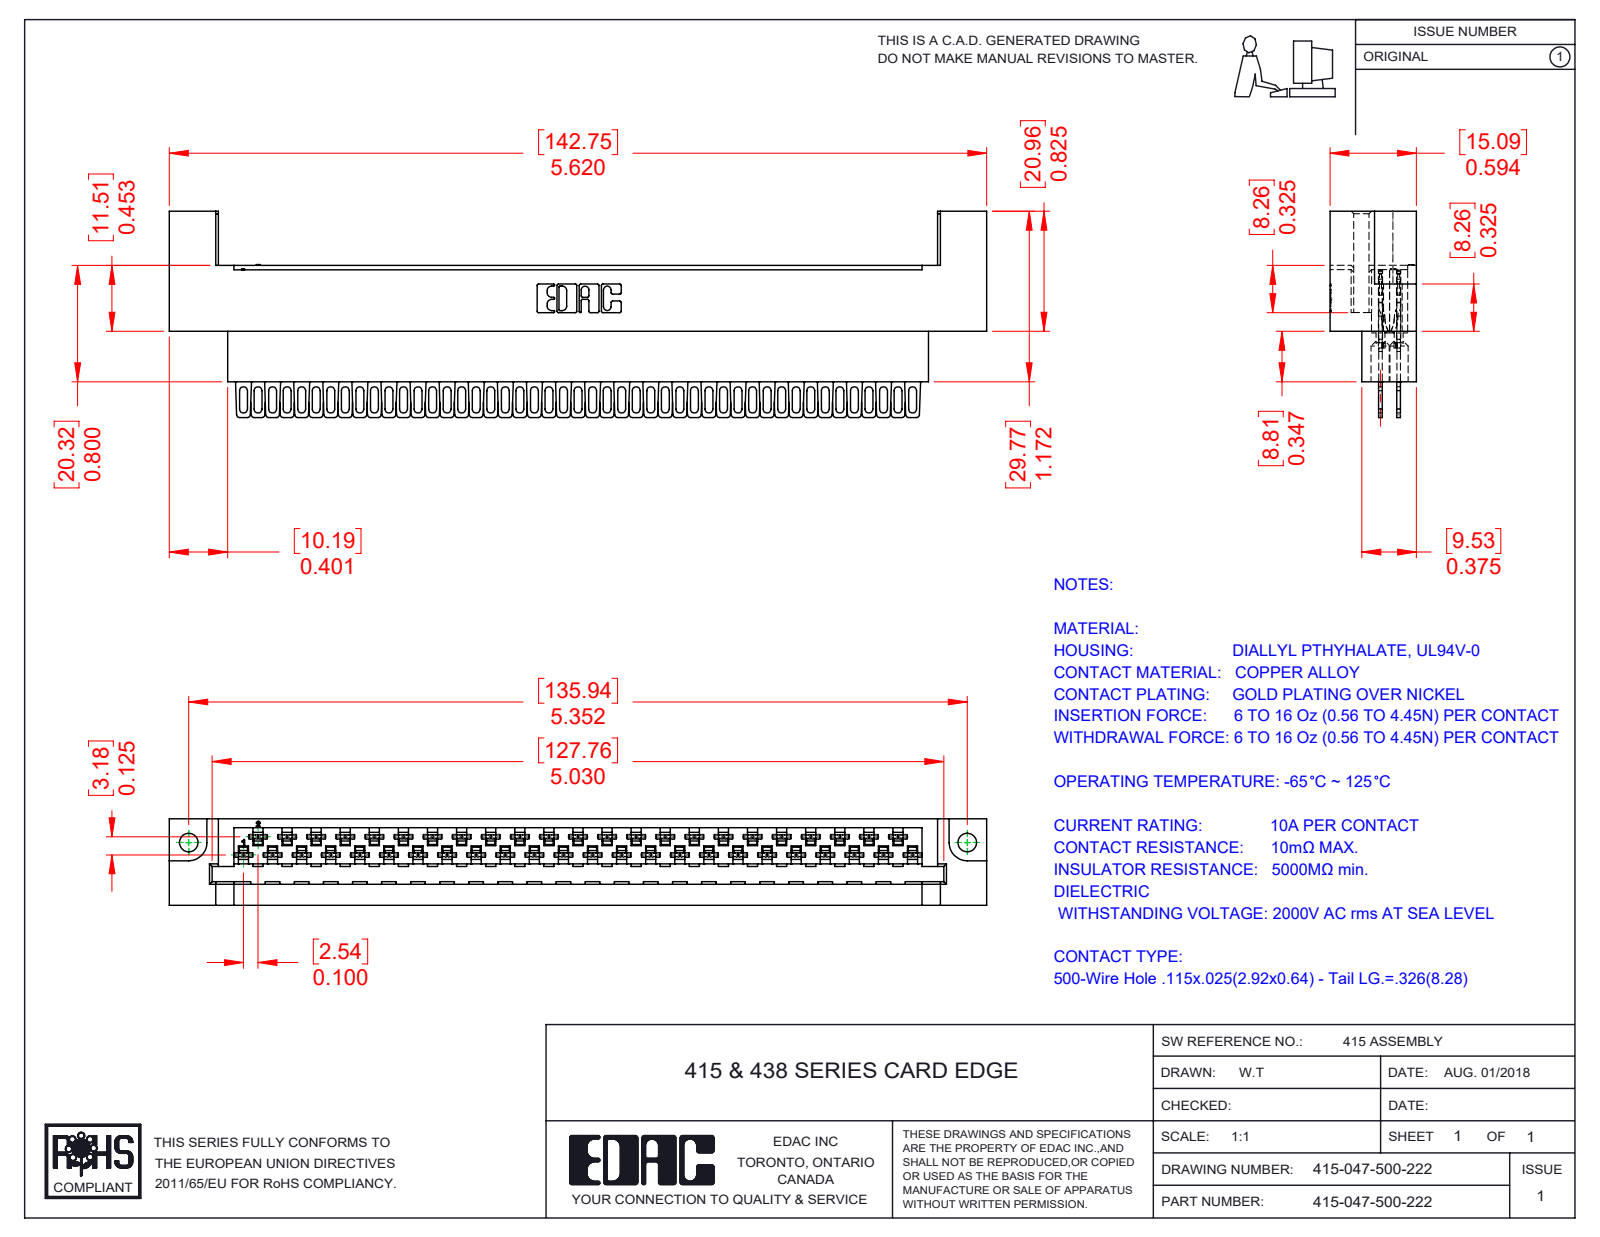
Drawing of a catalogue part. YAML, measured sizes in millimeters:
part_name: "415-047-500-222; 516-290-001_500; 415-210-001_415-210-047-222"
step_written_by: "SolidWorks 2016 (CONFIG_CONTROL_DESIGN)"
units: millimeters
bodies: {solids: 48, faces: 4956, planar: 3102, cylindrical: 1409, other: 445}
overall_size: [142.75, 36, 15.09]
volume: 27122
surface_area: 31647
round_holes:
  - {diameter: 1.27, count: 47}
  - {diameter: 3.3, count: 47}
  - {diameter: 3.25, count: 2}
partial_cylinders:
  - {radius: 0.3, count: 188}
  - {radius: 0.56, count: 188}
  - {radius: 0.18, count: 94}
  - {radius: 0.2, count: 94}
  - {radius: 0.41, count: 94}
  - {radius: 0.51, count: 94}
  - {radius: 0.69, count: 94}
  - {radius: 2.03, count: 94}
face_to_face_distances: [3.18, 0.61, 15.09, 1.27, 1.88, 1.94, 0.67, 6.61, 8.48, 6]
hole_center_spacings: [5.08, 10.16, 15.24, 20.32, 25.4, 30.48, 35.56, 2.54]
